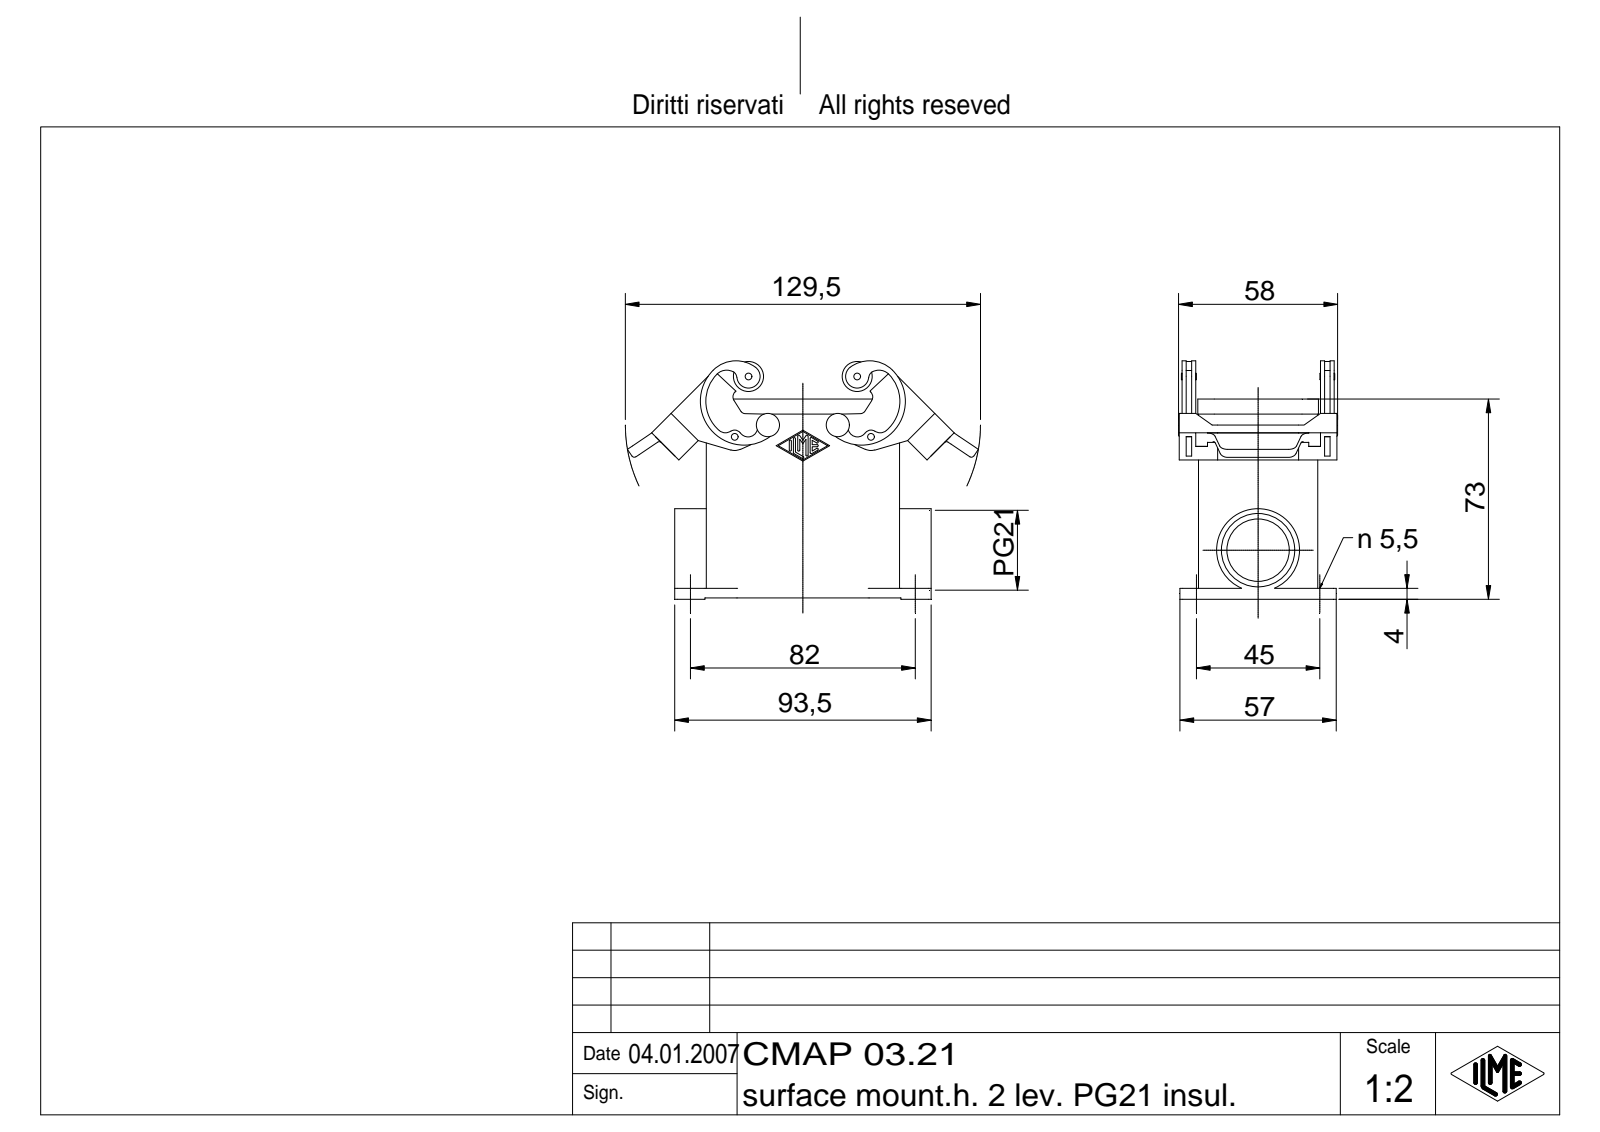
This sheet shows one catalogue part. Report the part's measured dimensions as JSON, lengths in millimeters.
{"part_name": "CMAP 03.21", "step_written_by": "Autodesk Inventor 7 (AUTOMOTIVE_DESIGN)", "units": "millimeters", "bodies": {"solids": 1, "faces": 749, "planar": 189, "cylindrical": 207, "other": 353}, "overall_size": [127.99, 86.94, 58], "volume_mm3": 105184, "surface_area_mm2": 58810, "round_holes": [[2, 4], [5.5, 4], [2.5, 2], [22.78, 1], [26.78, 1]], "round_bosses_or_shafts": [[11, 2], [5, 2], [3, 2], [30.28, 1]], "partial_cylinders_radius": [[1, 20], [0.38, 14], [3, 12], [6, 8], [2.5, 6], [1.5, 4], [2, 4], [3.5, 4]], "face_to_face_distances": [3, 40.5, 43.5, 3.5, 37.5, 4, 50.5, 11, 0.75, 59.5], "hole_center_spacings": [22.56, 45, 49.78, 82, 93.54, 39.64, 49.68]}
